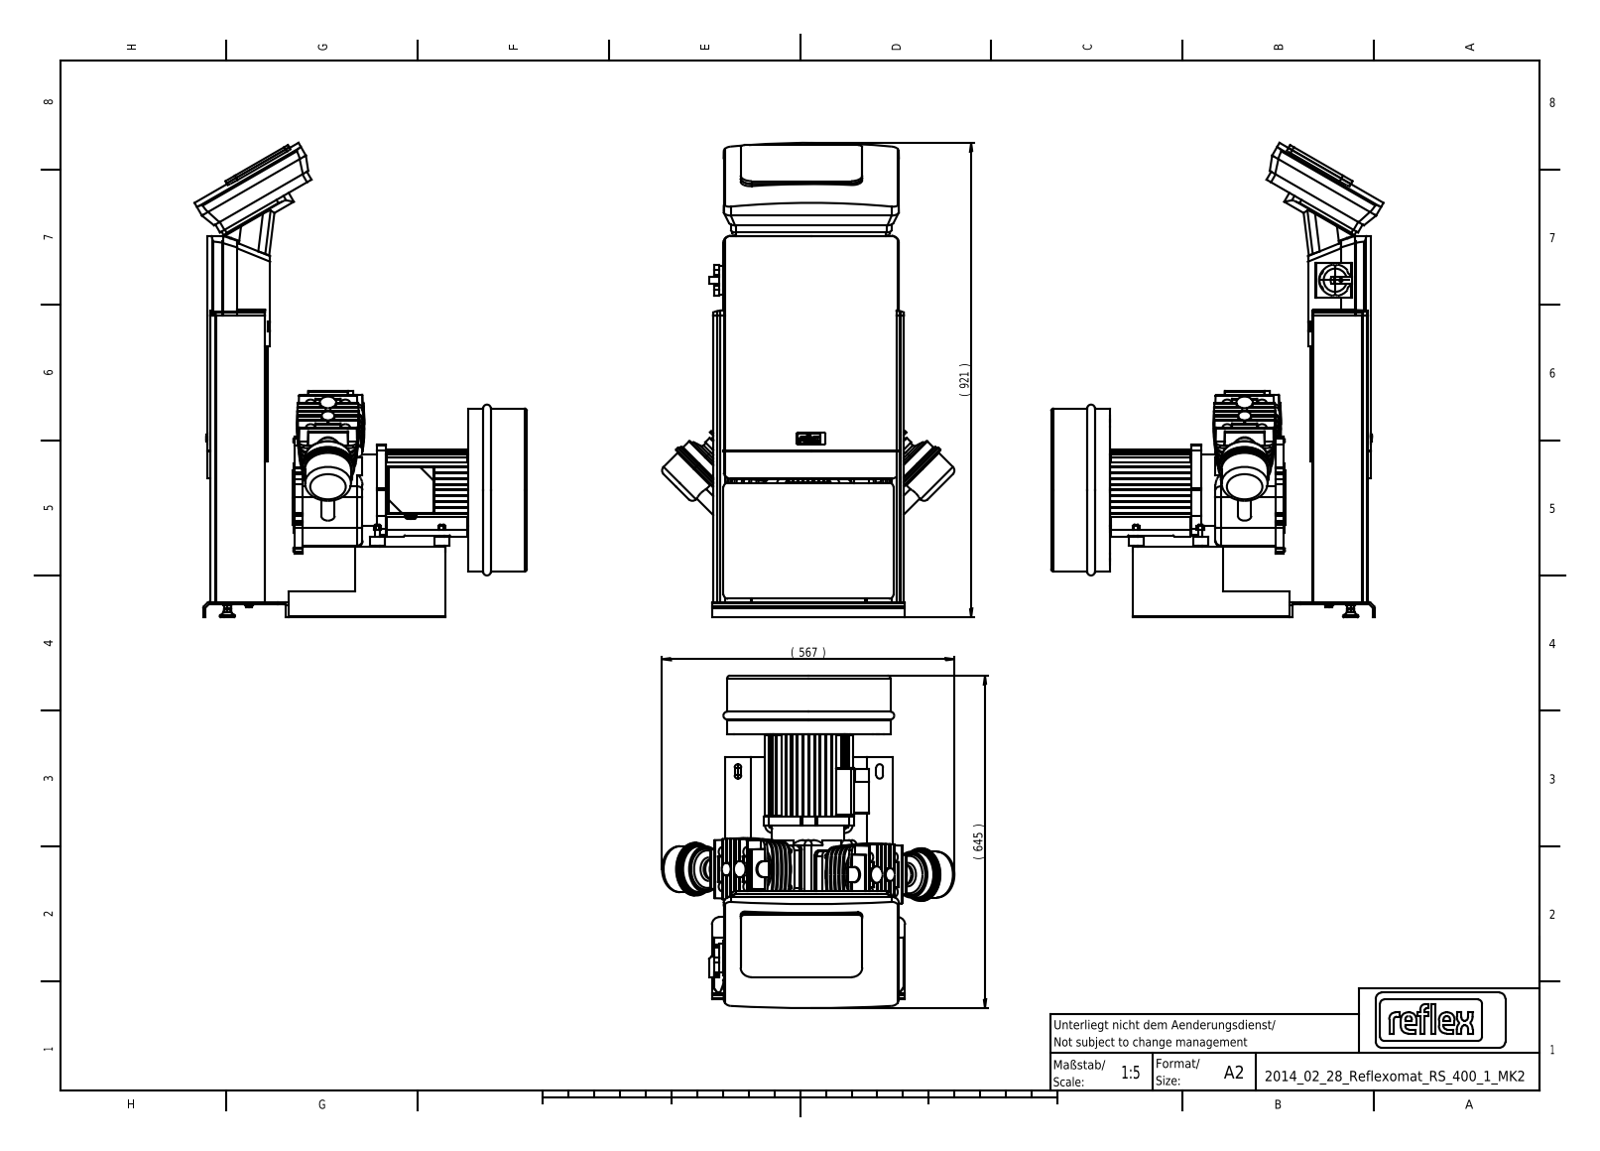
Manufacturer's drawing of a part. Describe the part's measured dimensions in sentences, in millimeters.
Its 3-D file was written by "Mechanical Desktop 2011 (CONFIG_CONTROL_DESIGN)". It is 100 solids with 5085 faces: 2271 planar, 982 cylindrical and 1832 other. Overall it measures 920.68 by 644.99 by 567.31 millimeters. Its volume is 38 970 000 cubic millimeters and its surface area 4 031 000 square millimeters. Round holes: 14 of diameter 7, 13 of diameter 17.5, 9 of diameter 10.5, 8 of diameter 17, 6 of diameter 5.5, 4 of diameter 9, 4 of diameter 13.5, 3 of diameter 5.4, 3 of diameter 20.5, 2 of diameter 23, 1 of diameter 6.2, 1 of diameter 6.4. Round bosses or shafts: 12 of diameter 16, 12 of diameter 8, 9 of diameter 19, 9 of diameter 11.2, 9 of diameter 5.1, 8 of diameter 20, 8 of diameter 17.5, 7 of diameter 7. Partial cylindrical surfaces (rounded edges, fillets, slot ends): 31 of radius 10, 27 of radius 3, 25 of radius 1, 16 of radius 5, 12 of radius 2, 7 of radius 6.5, 6 of radius 4.25, 6 of radius 4.5. The main face-to-face distances are 3, 10, 486.31, 476.31, 92, 102, 384.31, 2, 346.02, 12.5. The hole center spacings are 31, 62, 45, 89.08, 25.36, 36, 93, 48.65.
